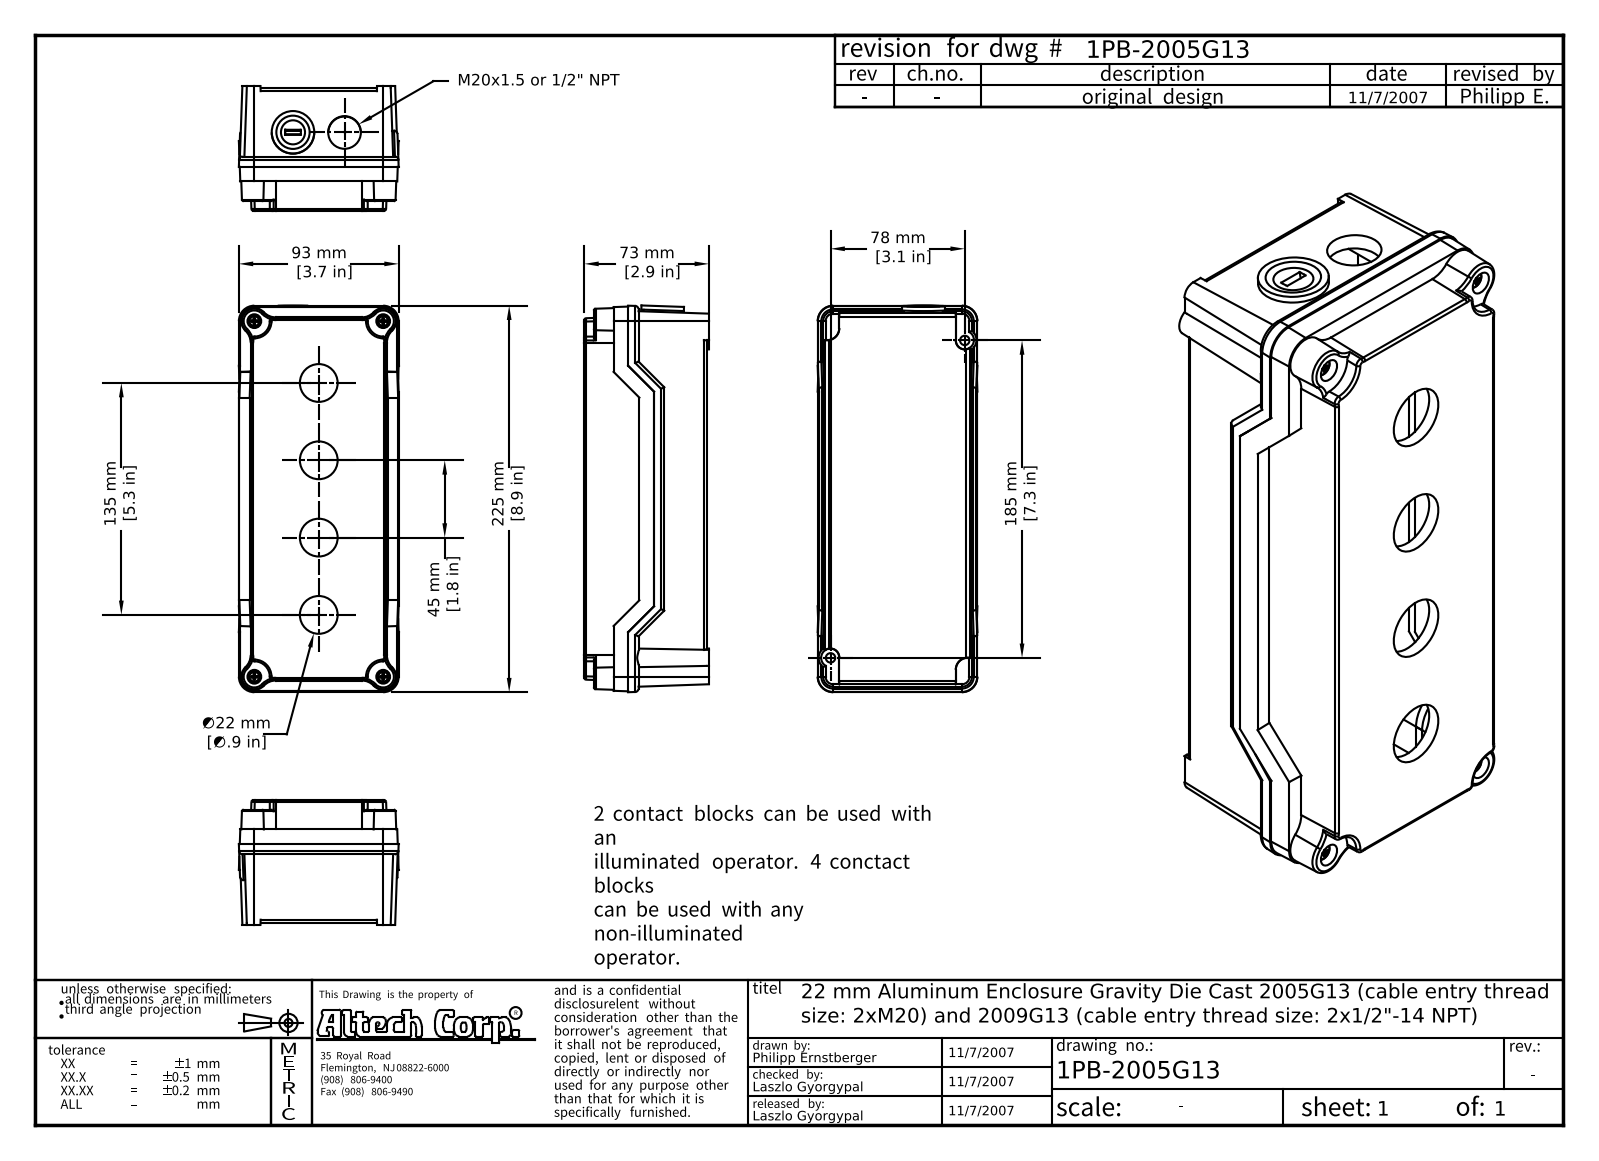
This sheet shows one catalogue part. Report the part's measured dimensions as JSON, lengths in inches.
{"part_name": "2005G13; enclosure_back; enclosure_front; DIN 125-1 B B 4 (+4 more)", "step_written_by": "Autodesk Inventor 2008 (AUTOMOTIVE_DESIGN)", "units": "inches", "bodies": {"solids": 12, "faces": 515, "planar": 204, "cylindrical": 77, "other": 234}, "overall_size": [8.863, 3.661, 2.854], "volume_in3": 25.61, "surface_area_in2": 260.1, "round_holes": [[0.138, 4], [0.866, 4], [0.169, 2], [0.748, 2]], "round_bosses_or_shafts": [[0.125, 4], [0.354, 2], [0.157, 2], [0.143, 2], [0.974, 1]], "partial_cylinders_radius": [[0.079, 22], [0.354, 6], [0.039, 4], [0.236, 2], [0.335, 2], [0.453, 2], [0.472, 2], [0.305, 1]], "face_to_face_distances": [2.579, 0.236, 2.815, 2.638, 0.177, 2.402, 2.913, 1.575, 1.004, 0.827], "hole_center_spacings": [2.046, 3.514, 5.176, 6.892, 1.772, 1.201, 1.319, 2.385]}
